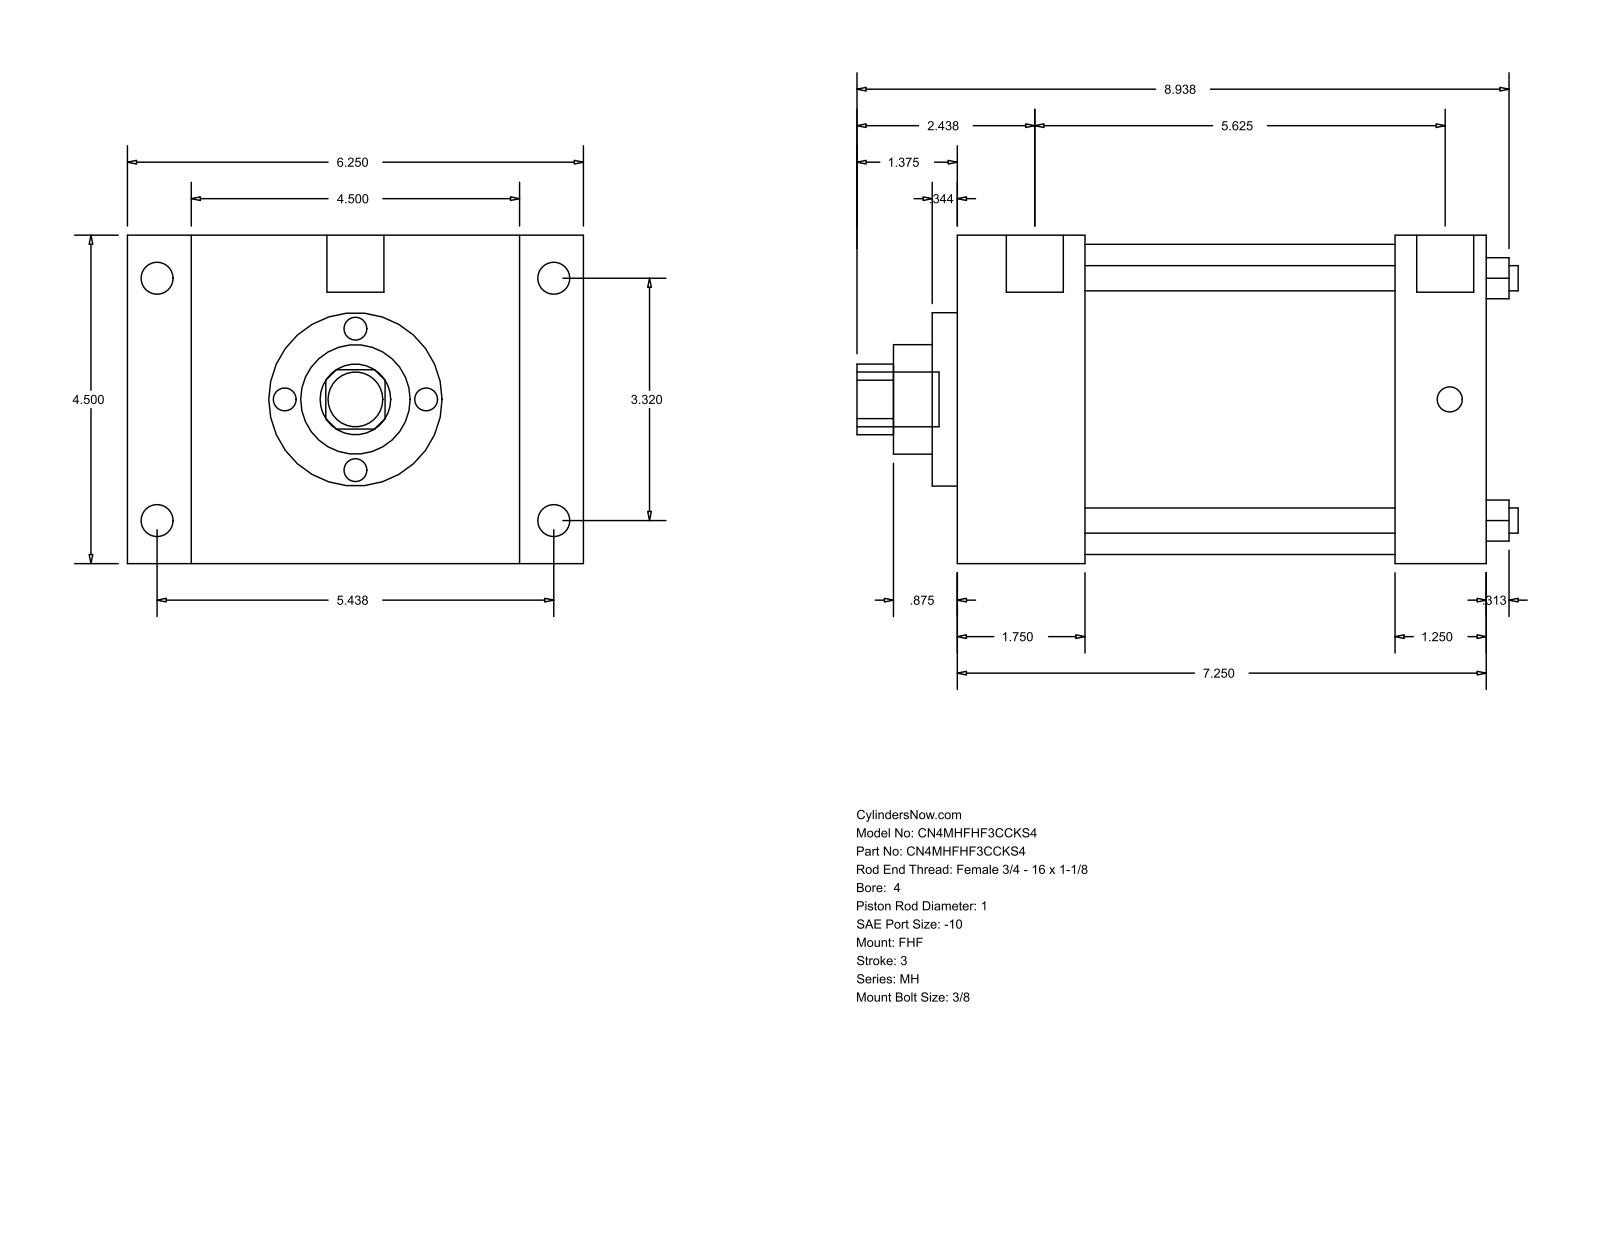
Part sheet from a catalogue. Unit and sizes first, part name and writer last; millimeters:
Units: millimetres
Overall size (bounding box): 230.19 × 158.75 × 114.3
Round holes (diameter × count): ⌀8.76 ×4, ⌀25.4 ×1, ⌀38.1 ×1, ⌀60.33 ×1, ⌀107.95 ×1
Round bosses / shafts (diameter × count): ⌀11.13 ×4, ⌀8.73 ×4, ⌀19.84 ×2, ⌀19.05 ×1
Partial cylindrical surfaces — rounded edges, fillets, slot ends (radius × count): R12.29 ×1
Main face-to-face distances: 114.3, 184.15, 44.46, 139.69, 22.23, 136.53, 158.76, 152.4, 107.94, 31.75
Hole centre spacings: 59.62, 84.32, 119.25
Bodies: 0 solids, 90 faces (61 planar, 29 cylindrical, 0 other)
Part name (STEP PRODUCT): MH_FHF__0400_1
STEP written by: GSSL Pune (CONFIG_CONTROL_DESIGN)
